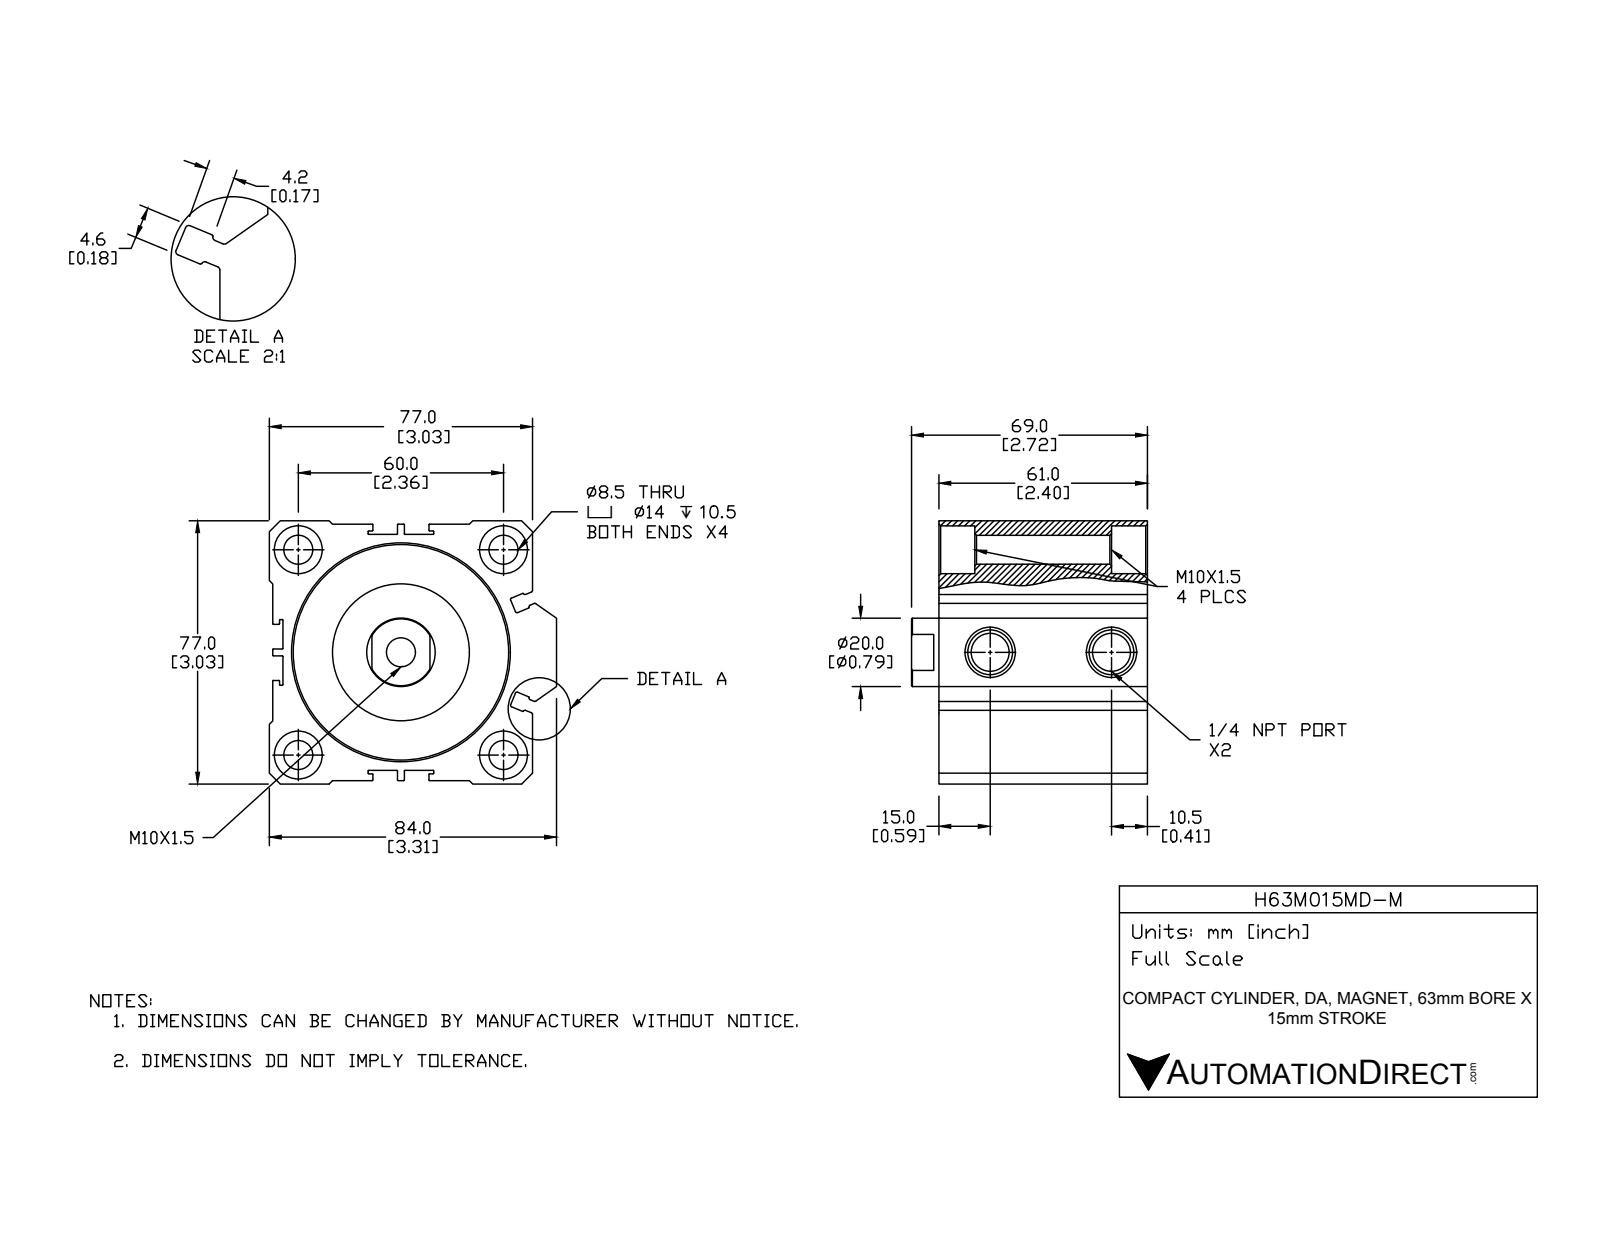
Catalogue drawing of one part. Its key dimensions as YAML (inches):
part_name: "H63M015MD-M; H63M015MD-M-PISTON; H63M015MD-M-BODY"
step_written_by: "SolidWorks 2015 (CONFIG_CONTROL_DESIGN)"
units: inches
bodies: {solids: 2, faces: 255, planar: 99, cylindrical: 103, other: 53}
overall_size: [3.307, 3.031, 2.717]
volume: 16.32
surface_area: 113.8
round_holes:
  - {diameter: 0.335, count: 5}
  - {diameter: 0.551, count: 4}
  - {diameter: 0.438, count: 2}
  - {diameter: 0.787, count: 1}
  - {diameter: 1.792, count: 1}
  - {diameter: 2.48, count: 1}
round_bosses_or_shafts:
  - {diameter: 1.575, count: 1}
  - {diameter: 1.535, count: 1}
partial_cylinders:
  - {radius: 0.008, count: 40}
  - {radius: 0.02, count: 12}
face_to_face_distances: [0.039, 2.992, 1.201, 0.118, 1.516, 3.031, 0.157, 2.874, 0.906, 0.61]
hole_center_spacings: [1.67, 2.362, 3.341, 1.398]
